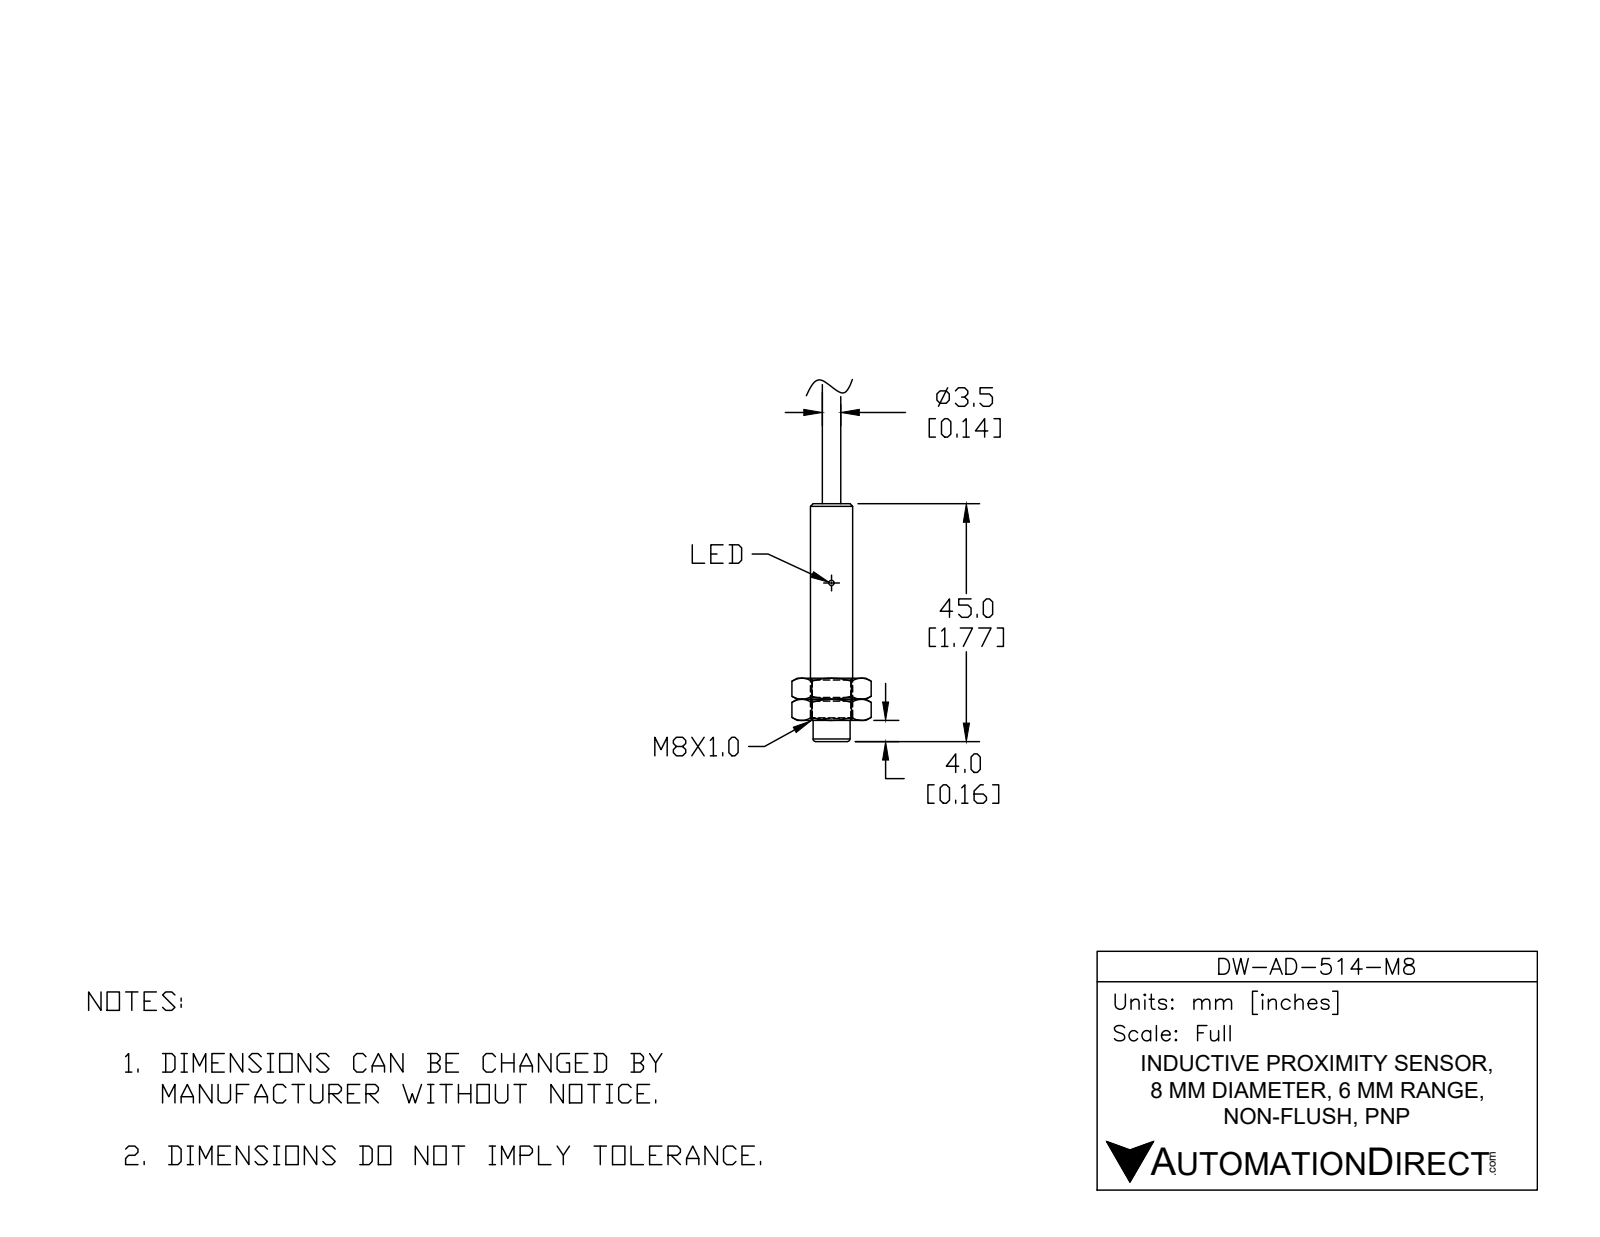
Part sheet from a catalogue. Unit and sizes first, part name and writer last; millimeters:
Units: millimetres
Overall size (bounding box): 71.2 × 8 × 8
Round bosses / shafts (diameter × count): ⌀8 ×1, ⌀6.9 ×1, ⌀6.5 ×1, ⌀5 ×1
Main face-to-face distances: 4.2, 71.2, 67, 45.5, 41.3, 25.7, 45, 40.8, 0.5, 26.2
Volume: 2 720 mm³ · Surface area: 1 688 mm²
Bodies: 2 solids, 14 faces (6 planar, 4 cylindrical, 4 other)
Part name (STEP PRODUCT): DW-AD-514-M8
STEP written by: SolidWorks 2017 (AUTOMOTIVE_DESIGN)
